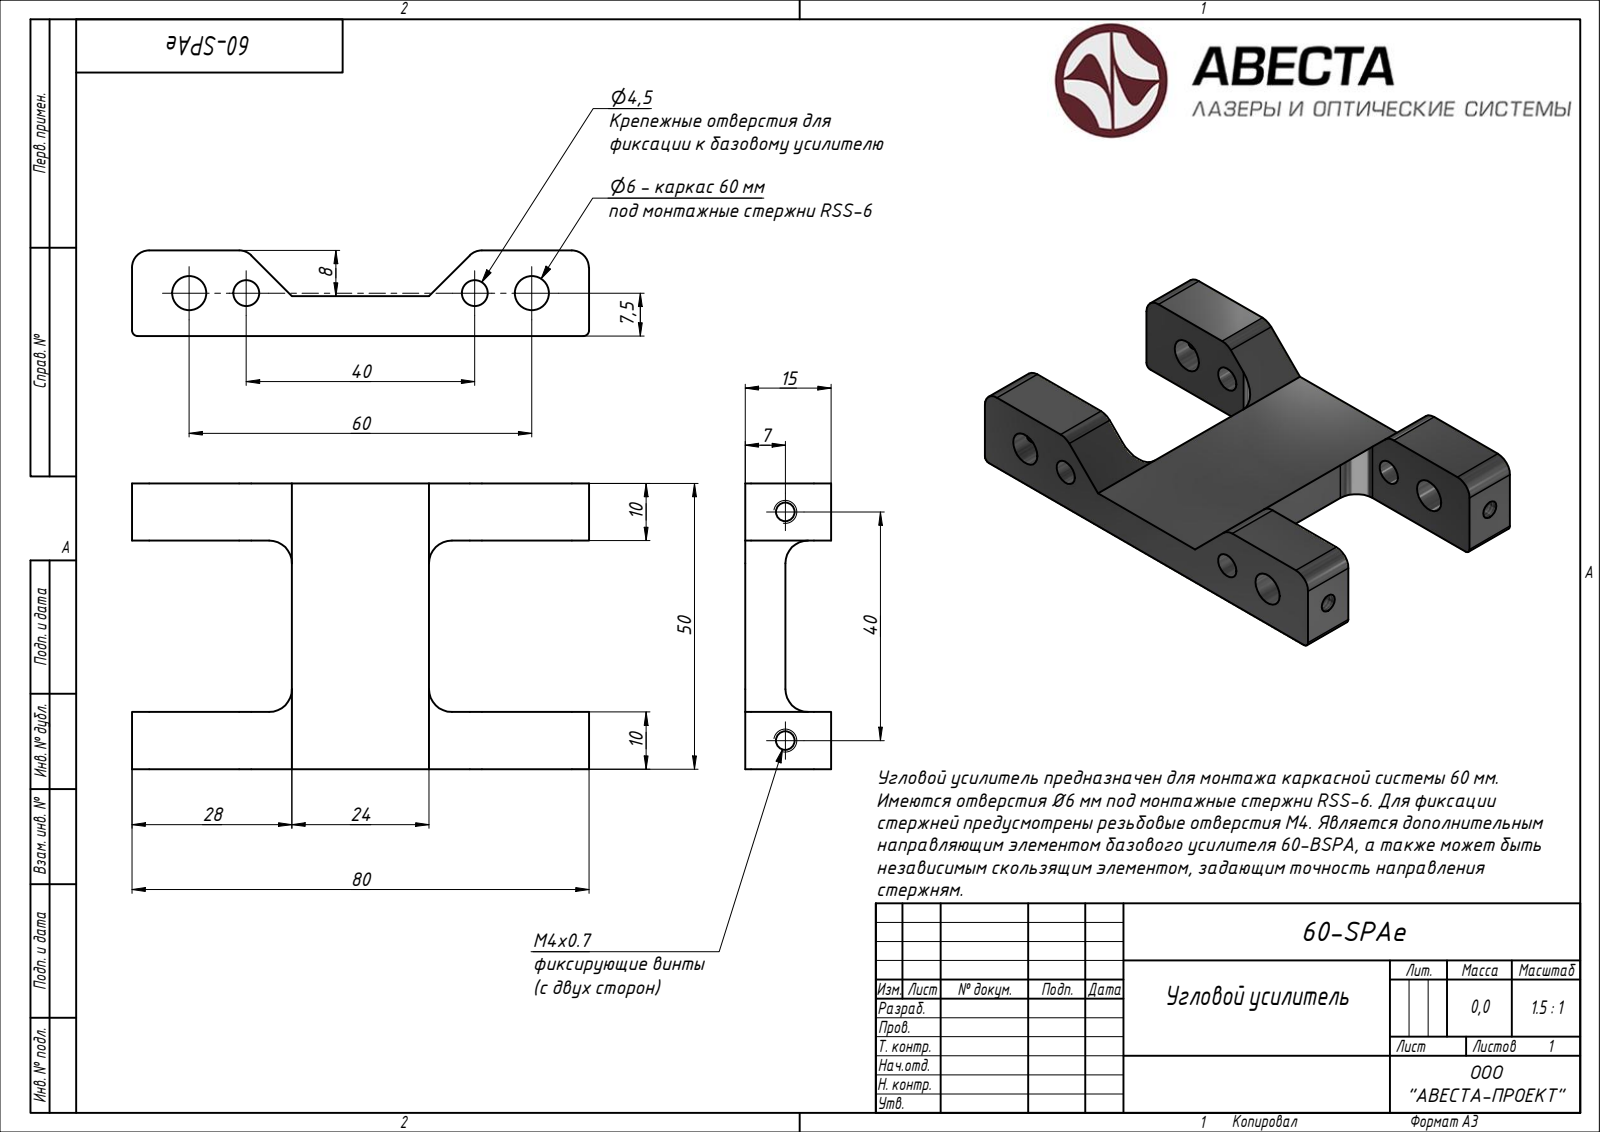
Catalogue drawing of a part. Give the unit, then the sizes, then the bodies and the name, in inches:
Units: inches
Overall size (bounding box): 3.15 × 1.969 × 0.591
Main face-to-face distances: 0.394, 1.575, 0.276, 1.969, 0.591, 0.315, 1.181, 1.102, 2.047, 3.15
Volume: 1.338 in³ · Surface area: 16.01 in²
Bodies: 1 solid, 62 faces (22 planar, 0 cylindrical, 40 other)
STEP written by: ST-DEVELOPER v15 (AUTOMOTIVE_DESIGN)
